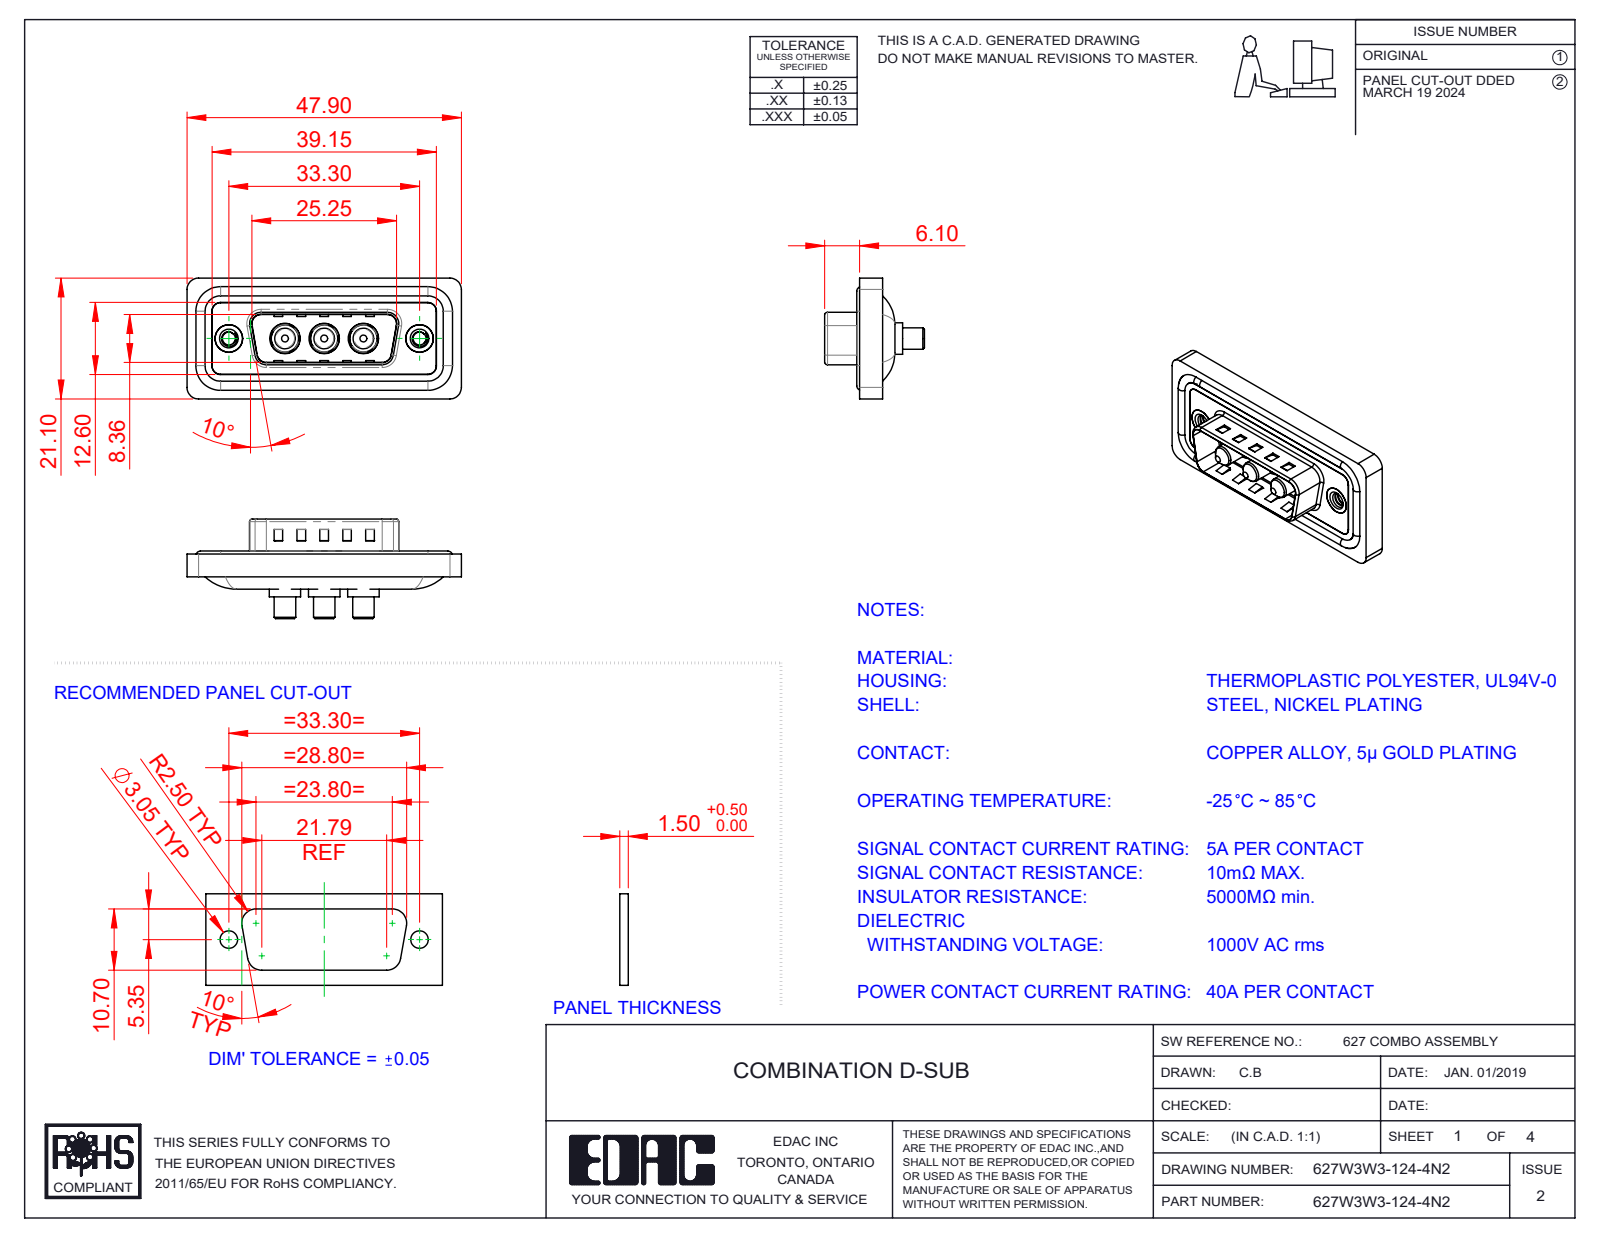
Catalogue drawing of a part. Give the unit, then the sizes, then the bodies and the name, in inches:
Units: inches
Overall size (bounding box): 1.886 × 0.831 × 0.685
Round holes (diameter × count): ⌀0.191 ×3, ⌀0.209 ×3, ⌀0.089 ×2, ⌀0.157 ×2, ⌀0.189 ×2, ⌀0.197 ×2
Round bosses / shafts (diameter × count): ⌀0.063 ×4, ⌀0.217 ×3, ⌀0.205 ×3, ⌀0.187 ×3, ⌀0.148 ×3, ⌀0.142 ×3, ⌀0.193 ×2
Partial cylindrical surfaces — rounded edges, fillets, slot ends (radius × count): R0.059 ×26, R0.079 ×20, R0.02 ×8, R0.063 ×8, R0.01 ×4, R0.024 ×4, R0.026 ×4, R0.035 ×4
Main face-to-face distances: 0.016, 0.043, 0.059, 0.02, 0.063, 0.122, 0.114, 0.157, 0.032, 0.377
Hole centre spacings: 0.27, 0.386, 0.656, 0.925, 0.539, 1.311
Volume: 0.344 in³ · Surface area: 13.62 in²
Bodies: 13 solids, 564 faces (207 planar, 241 cylindrical, 116 other)
Part name (STEP PRODUCT): 627Combo Threaded Rivet_2; 627Combo Housing_3W3; 627Combo Waterproof Housing_15 Contacts; Power Pin_40A S (+3 more)
STEP written by: SolidWorks 2023 (CONFIG_CONTROL_DESIGN)
